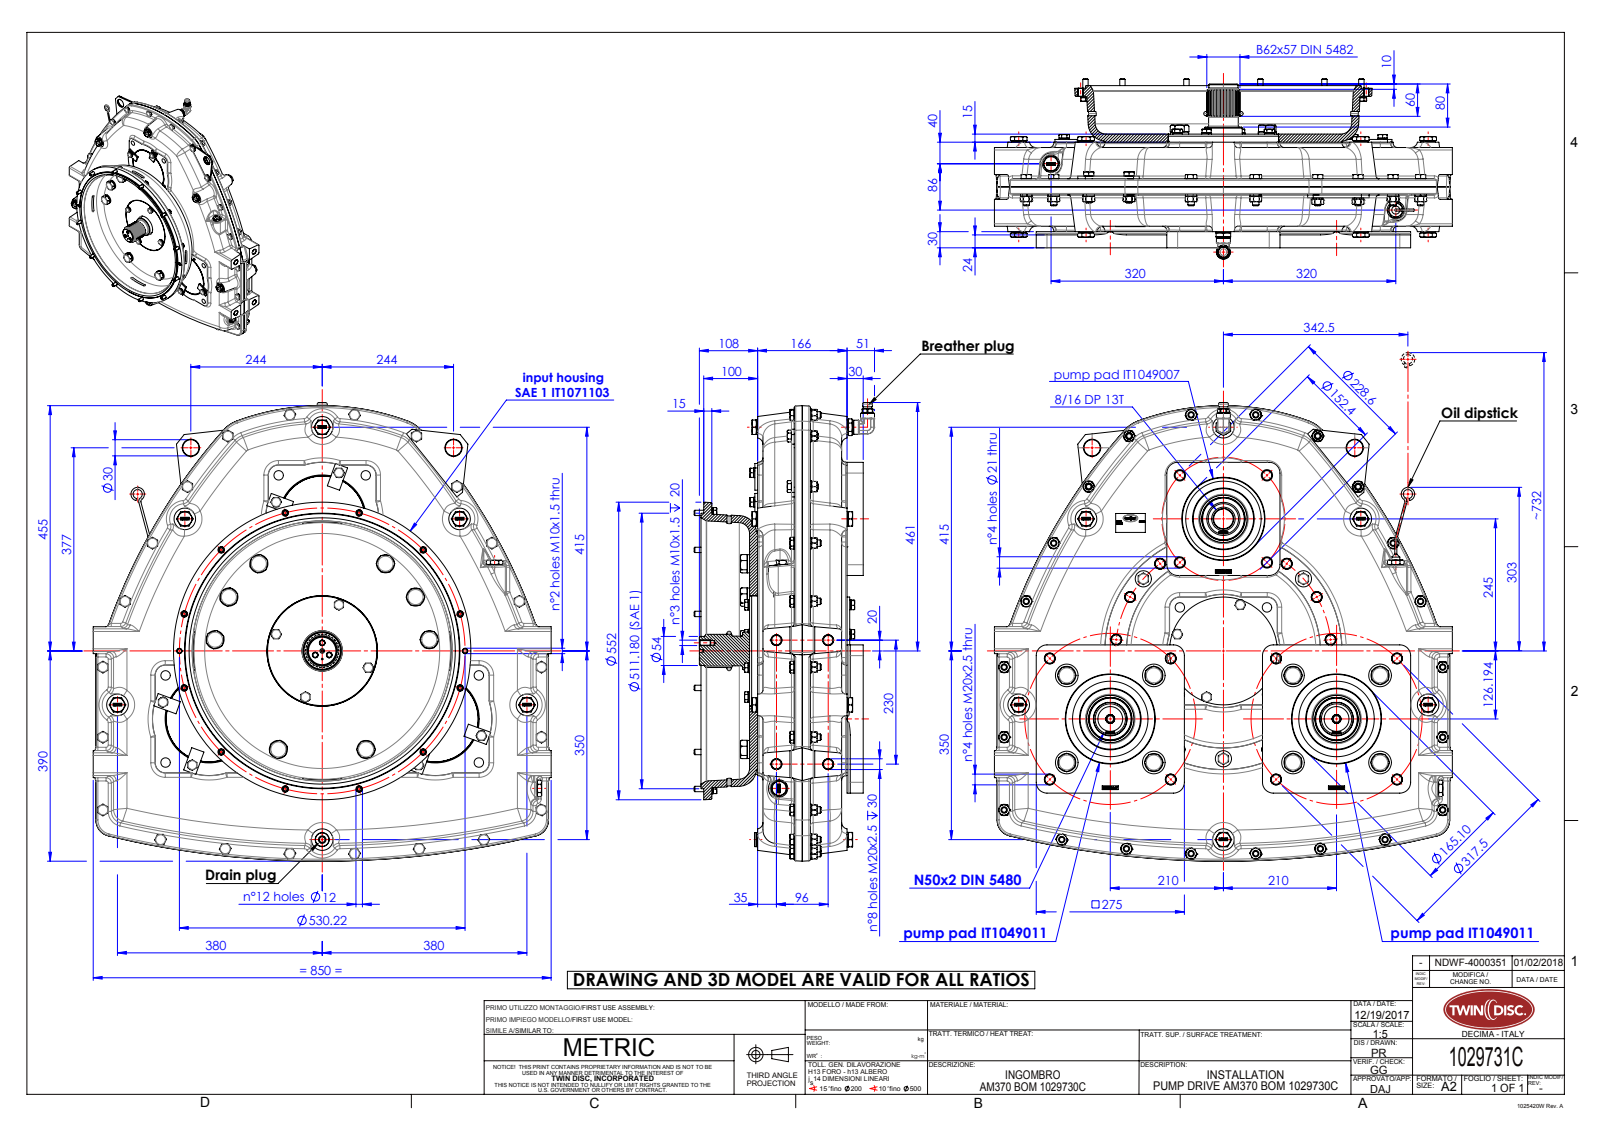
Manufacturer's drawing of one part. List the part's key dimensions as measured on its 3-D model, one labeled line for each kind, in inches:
Part name (STEP PRODUCT): IT1049007_rev00-installation; ITam270-012_rev00-installation; ITam370-002_rev00-installation; IT2021490_rev00-installation (+8 more)
STEP written by: SolidWorks 2015 (AUTOMOTIVE_DESIGN)
Units: inches
Bodies: 66 solids, 10527 faces (4405 planar, 3083 cylindrical, 3039 other)
Overall size (bounding box): 33.496 × 33.465 × 13.181
Volume: 790.9 in³ · Surface area: 9 832 in²
Round holes (diameter × count): ⌀0.335 ×37, ⌀0.689 ×36, ⌀0.827 ×30, ⌀0.512 ×28, ⌀0.402 ×25, ⌀0.48 ×25, ⌀0.406 ×21, ⌀0.472 ×17, ⌀0.795 ×16, ⌀0.433 ×14, ⌀0.787 ×12, ⌀0.733 ×10
Round bosses / shafts (diameter × count): ⌀0.394 ×28, ⌀0.831 ×25, ⌀0.713 ×25, ⌀0.709 ×25, ⌀0.638 ×25, ⌀0.472 ×21, ⌀1.323 ×16, ⌀1.142 ×16
Partial cylindrical surfaces — rounded edges, fillets, slot ends (radius × count): R0.014 ×274, R1.509 ×216, R0.018 ×58, R1.143 ×58, R1.163 ×58, R0.748 ×32, R0.236 ×30, R0.315 ×30
Main face-to-face distances: 3.268, 2.874, 6.142, 0.394, 0.591, 3.858, 1.181, 5.748, 6.535, 4.449
Hole centre spacings: 32.047, 4.5, 6.364, 27.059, 1.783, 2.106, 2.964, 3.78
